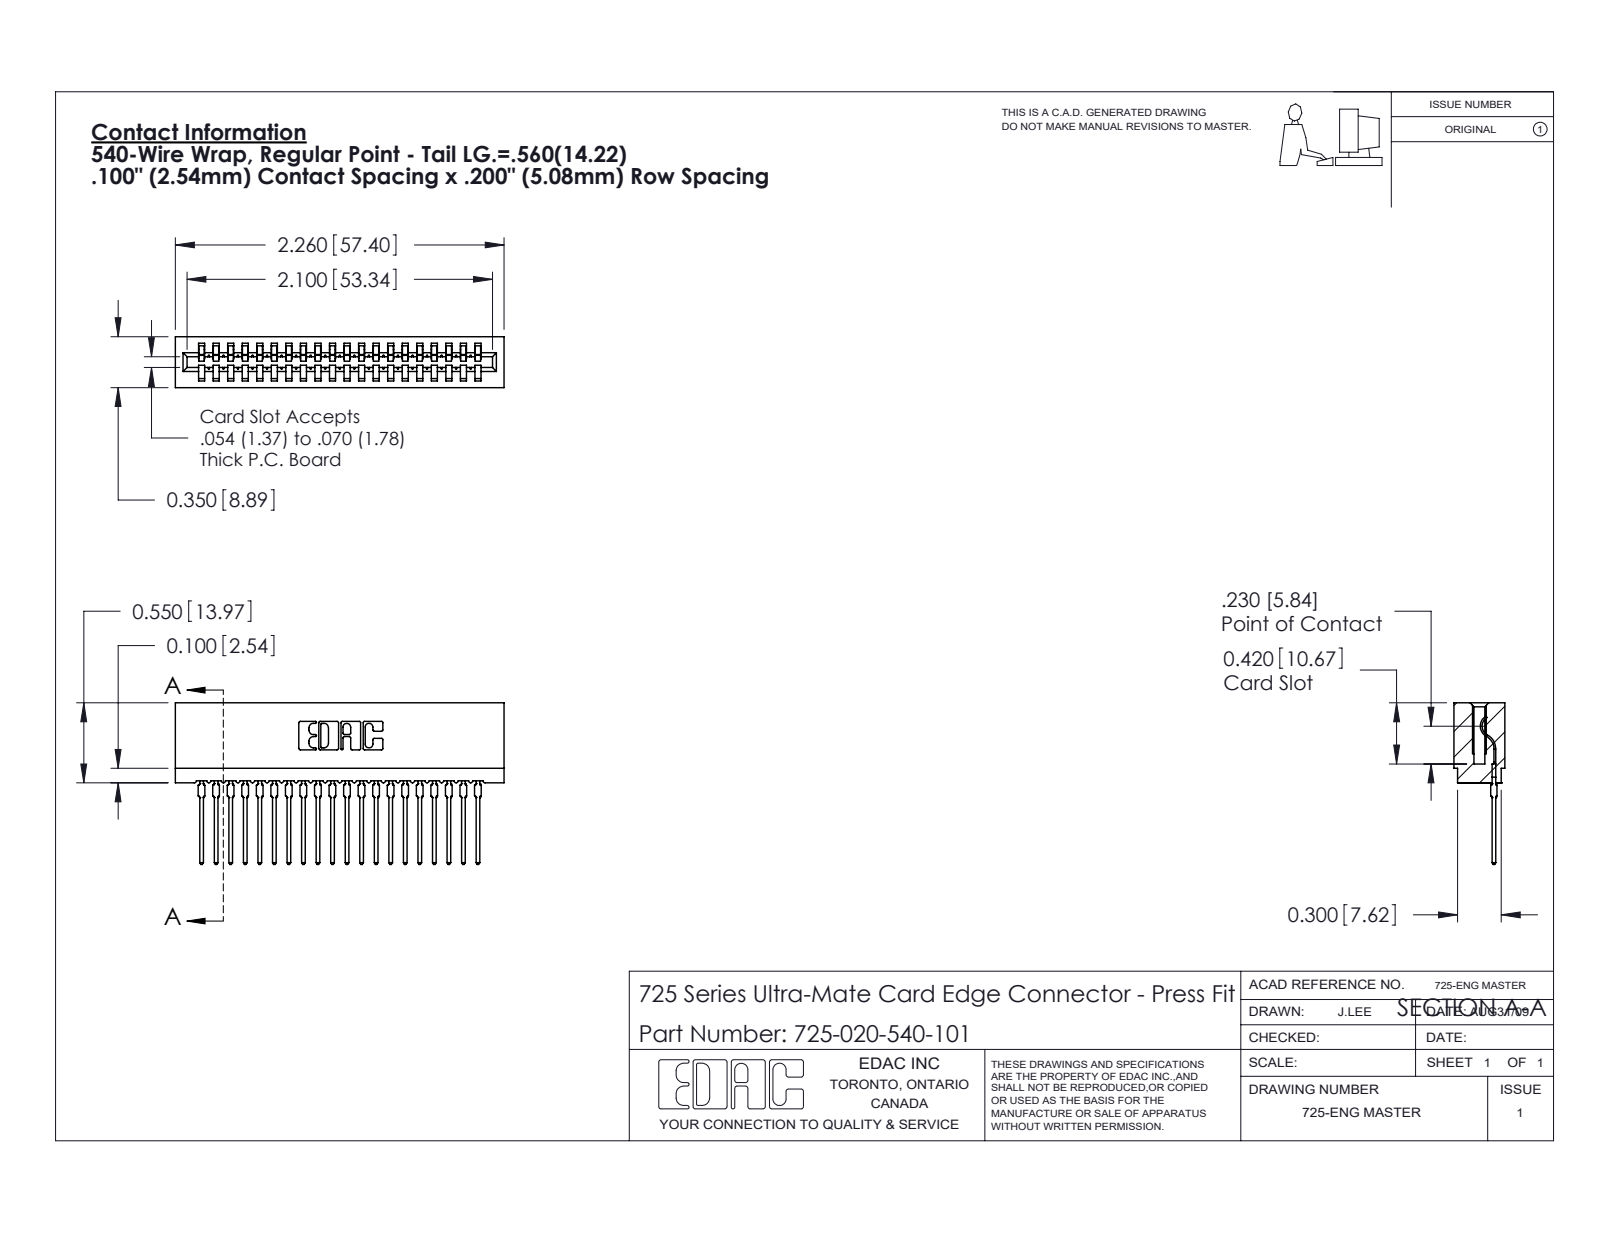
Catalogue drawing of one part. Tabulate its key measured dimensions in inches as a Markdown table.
| quantity | value |
| --- | --- |
| part name | 725 Part_Insulator Option - 01; 725-020-540-101; 745-292-001_540 |
| STEP written by | SolidWorks 2020 (CONFIG_CONTROL_DESIGN) |
| units | inches |
| bodies | 21 solids, 2335 faces (1395 planar, 420 cylindrical, 520 other) |
| overall size | 2.26 × 1.111 × 0.35 |
| volume | 0.276 in³ |
| surface area | 13.22 in² |
| partial cylindrical surfaces (radius × count) | 0.015 × 40, 0.021 × 40, 0.01 × 22, 0.007 × 6, 0.031 × 6, 0.005 × 4, 0.011 × 4, 0.026 × 3 |
| main face-to-face distances | 0.1, 0.2, 0.3, 0.4, 0.5, 0.6, 0.7, 0.35, 0.8, 0.212 |
